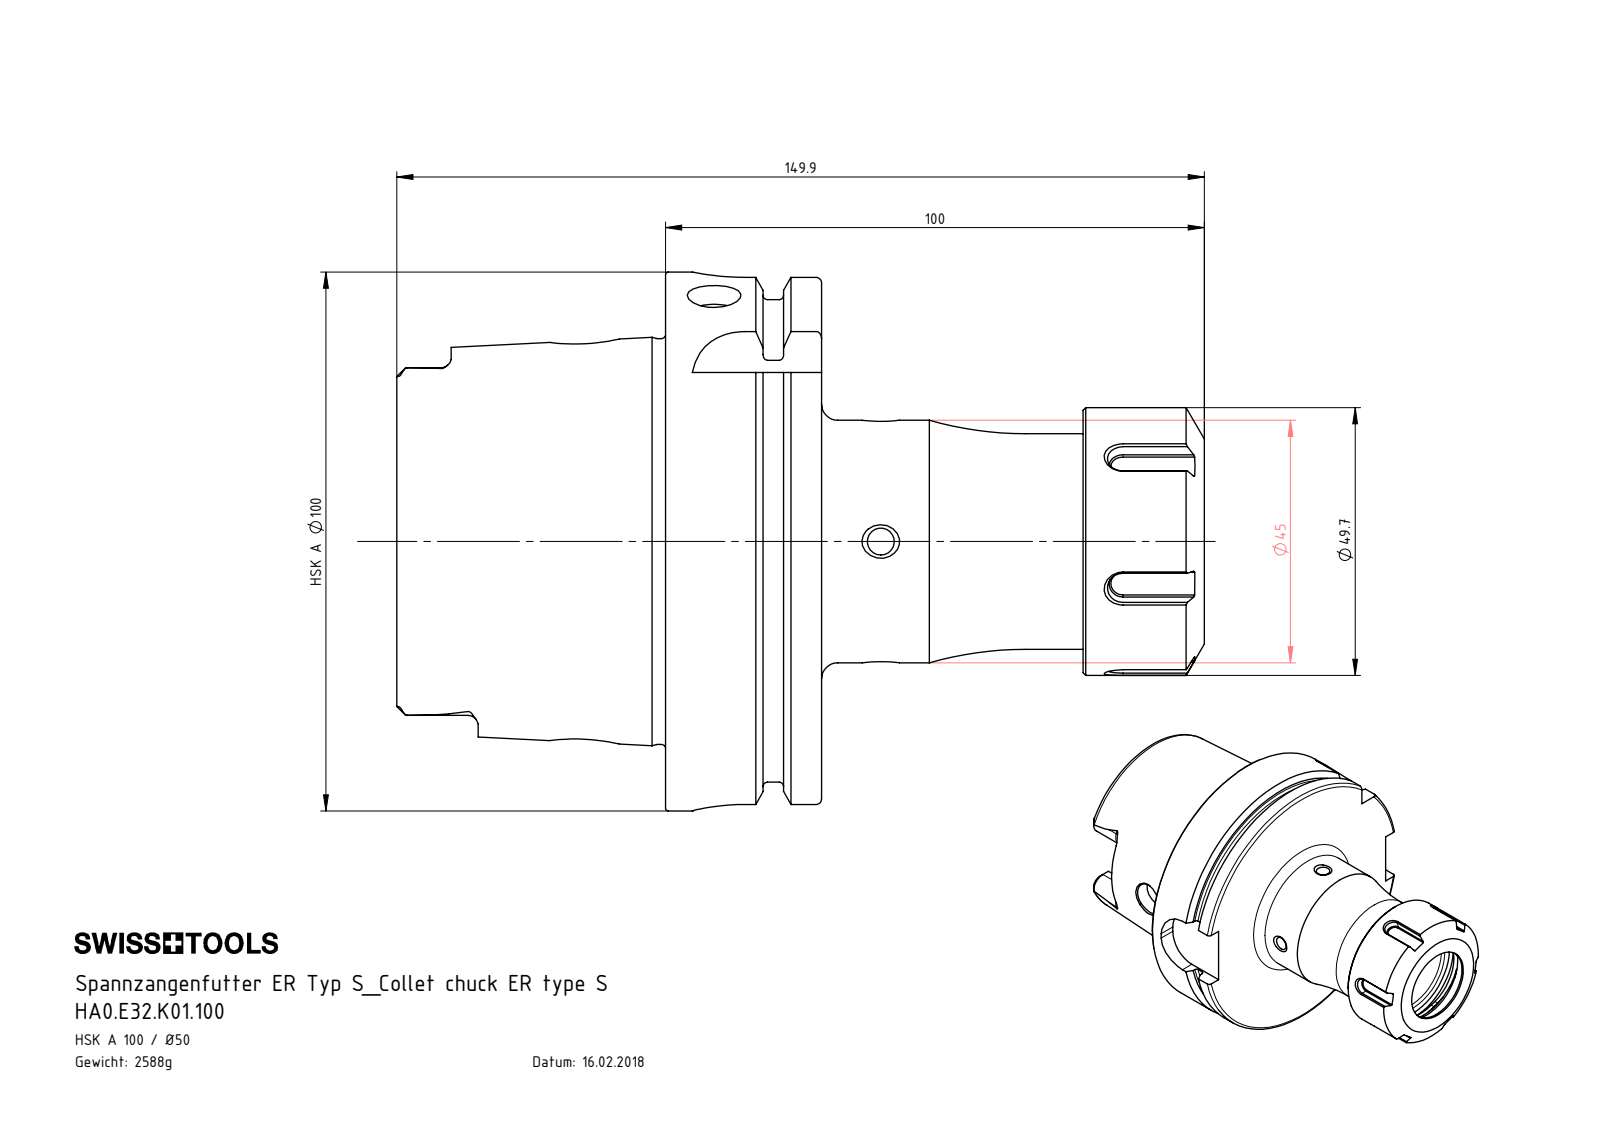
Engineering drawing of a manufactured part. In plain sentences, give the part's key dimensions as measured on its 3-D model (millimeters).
The part is named "E32-ER1.001.022; HA0-E32.K01.100_B_Fertigbearbeitung; HA0.E32.K01.100; ERU-AN5.K01.020_A". Its 3-D file was written by "SolidWorks 2017 (CONFIG_CONTROL_DESIGN)". It is 3 solids with 337 faces: 126 planar, 83 cylindrical and 128 other. Overall it measures 149.9 by 100 by 100 millimeters. Its volume is 329 434 cubic millimeters and its surface area 71 061 square millimeters. Round holes: 3 of diameter 10, 2 of diameter 5, 1 of diameter 6, 1 of diameter 11, 1 of diameter 12, 1 of diameter 22.5, 1 of diameter 23.5, 1 of diameter 26, 1 of diameter 27.1, 1 of diameter 38.5, 1 of diameter 40.5, 1 of diameter 53. Round bosses or shafts: 1 of diameter 100, 1 of diameter 91.95, 1 of diameter 75.26, 1 of diameter 49.7, 1 of diameter 45, 1 of diameter 40, 1 of diameter 12. Partial cylindrical surfaces (rounded edges, fillets, slot ends): 6 of radius 1.9, 4 of radius 4.88, 4 of radius 10, 2 of radius 15.5. The main face-to-face distances are 28.95, 12.45, 16.5, 49.9, 62.35, 78.85, 127.4, 77.5, 65.05, 48.55. The hole center spacings are 32.95, 54.95.
